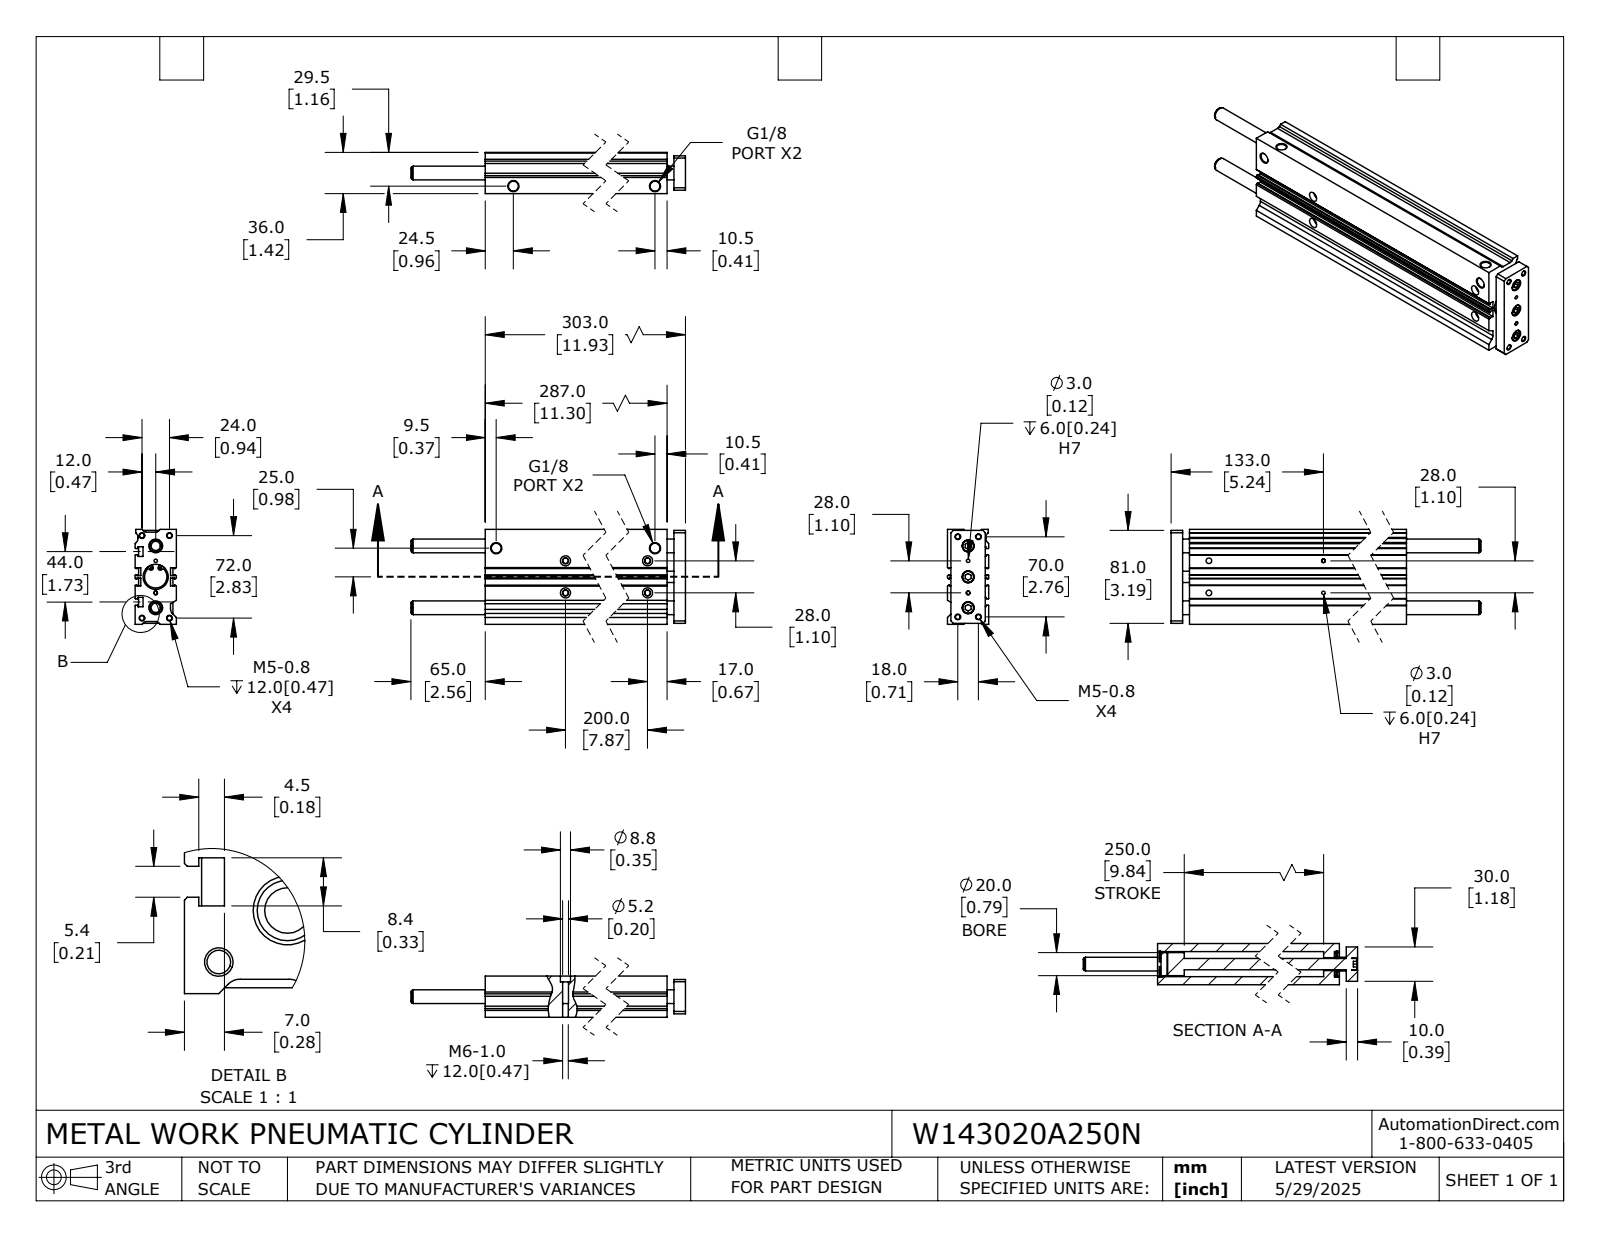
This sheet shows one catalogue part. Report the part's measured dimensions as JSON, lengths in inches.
{"part_name": "W143020A250N_ROD; W143020A250N; W143020A250N_BODY", "step_written_by": "SolidWorks 2024 (CONFIG_CONTROL_DESIGN)", "units": "inches", "bodies": {"solids": 6, "faces": 357, "planar": 174, "cylindrical": 145, "other": 38}, "overall_size": [14.488, 3.268, 1.417], "volume_in3": 43.06, "surface_area_in2": 300.5, "round_holes": [[0.163, 8], [0.079, 4], [0.118, 4], [0.205, 4], [0.337, 4], [0.346, 4], [0.413, 3], [0.194, 2], [0.194, 2], [0.472, 2], [0.449, 1], [0.767, 1]], "round_bosses_or_shafts": [[0.394, 3], [0.906, 2], [0.787, 1], [0.512, 1]], "partial_cylinders_radius": [[0.053, 4], [0.059, 4], [0.071, 4], [0.118, 4], [0.197, 3]], "face_to_face_distances": [1.417, 0.098, 0.197, 1.22, 0.079, 3.268, 3.169, 0.276, 0.945, 1.142], "hole_center_spacings": [0.124, 0.296, 0.336, 0.474, 0.591, 0.78, 0.828, 0.864]}
